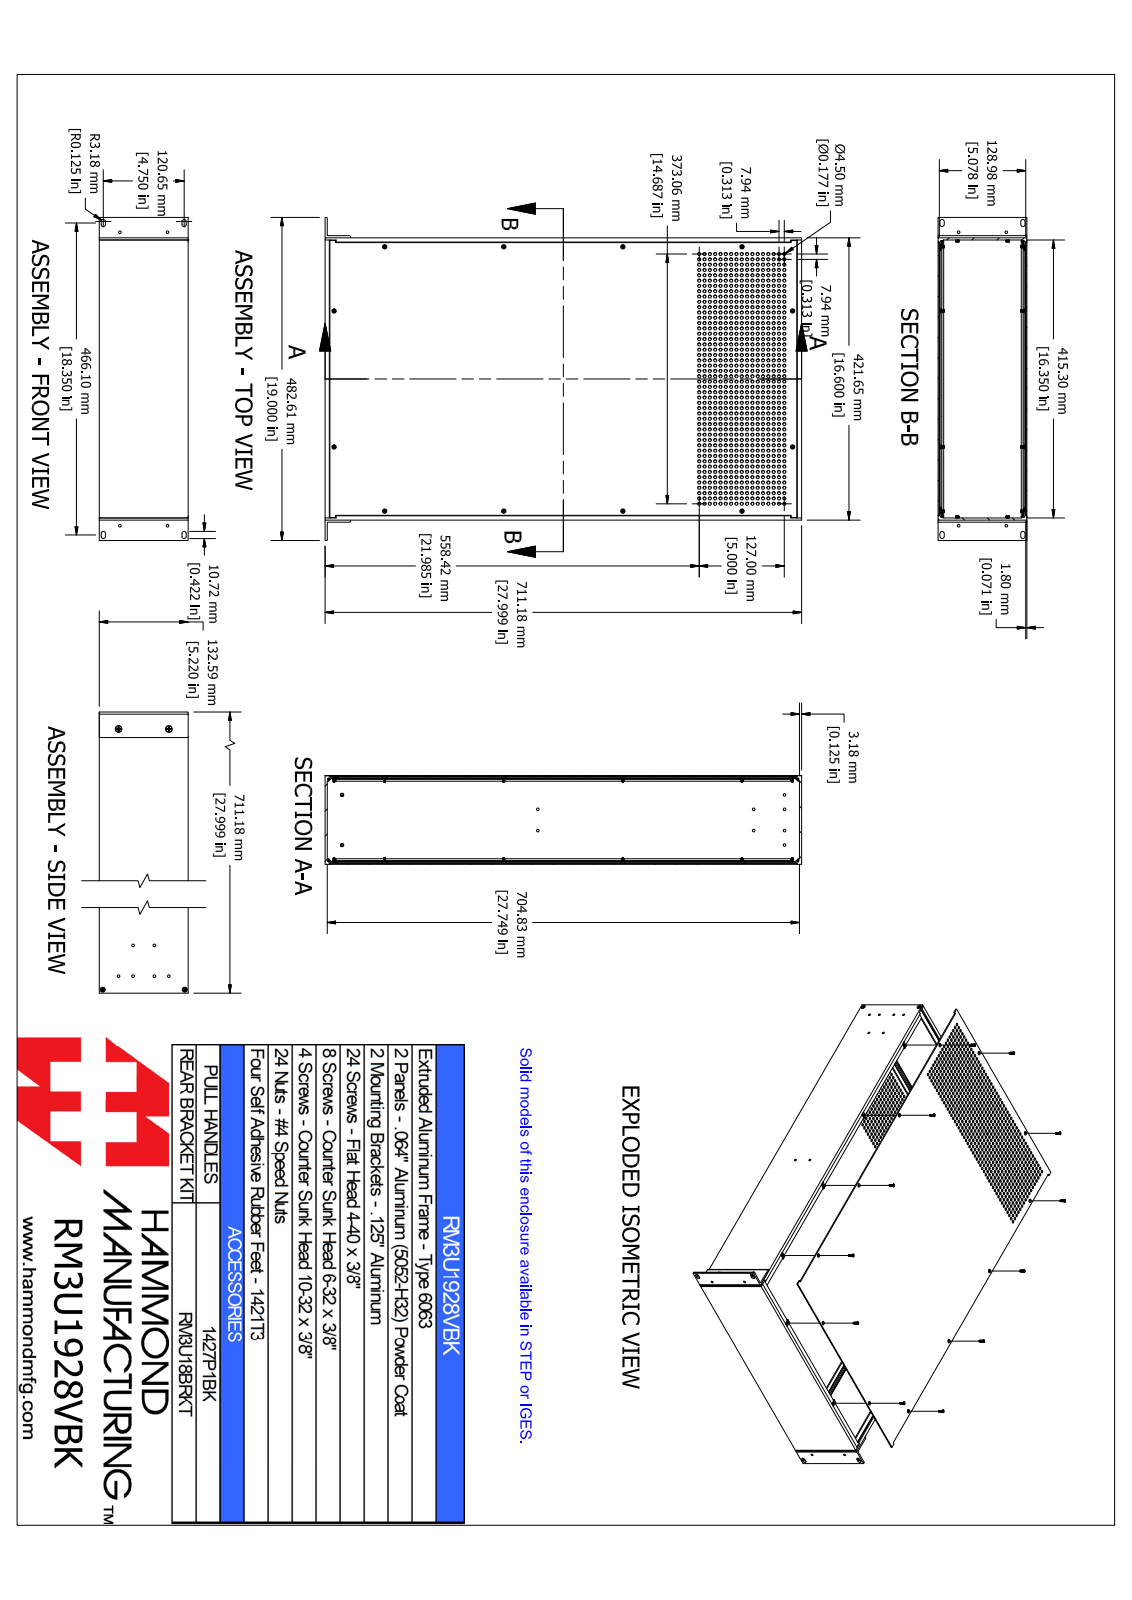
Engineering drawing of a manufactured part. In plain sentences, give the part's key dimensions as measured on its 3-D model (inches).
The part is named "RM3U1928VBK". Its 3-D file was written by "SolidWorks 2021 (AUTOMOTIVE_DESIGN)". It is 68 solids with 4268 faces: 1076 planar, 2260 cylindrical and 932 other. Overall it measures 28.164 by 19 by 5.221 inches. Its volume is 132.3 cubic inches and its surface area 3 001 square inches. Round holes: 1632 of diameter 0.177, 16 of diameter 0.157, 14 of diameter 0.16, 8 of diameter 0.165, 6 of diameter 0.159, 4 of diameter 0.156, 4 of diameter 0.157, 4 of diameter 0.169, 2 of diameter 0.197. Round bosses or shafts: 14 of diameter 0.2, 14 of diameter 0.112, 4 of diameter 0.238, 4 of diameter 0.138, 2 of diameter 0.36, 2 of diameter 0.19. Partial cylindrical surfaces (rounded edges, fillets, slot ends): 96 of radius 0.01, 96 of radius 0.024, 48 of radius 0.009, 48 of radius 0.014, 17 of radius 0.039, 16 of radius 0.015, 16 of radius 0.038, 11 of radius 0.035. The main face-to-face distances are 5.149, 0.071, 5.22, 5.078, 0.125, 16.476, 16.601, 16.35, 0.125, 27.999. The hole center spacings are 7, 17.049, 14, 20.92, 26.707, 4.803, 8, 10.662.
